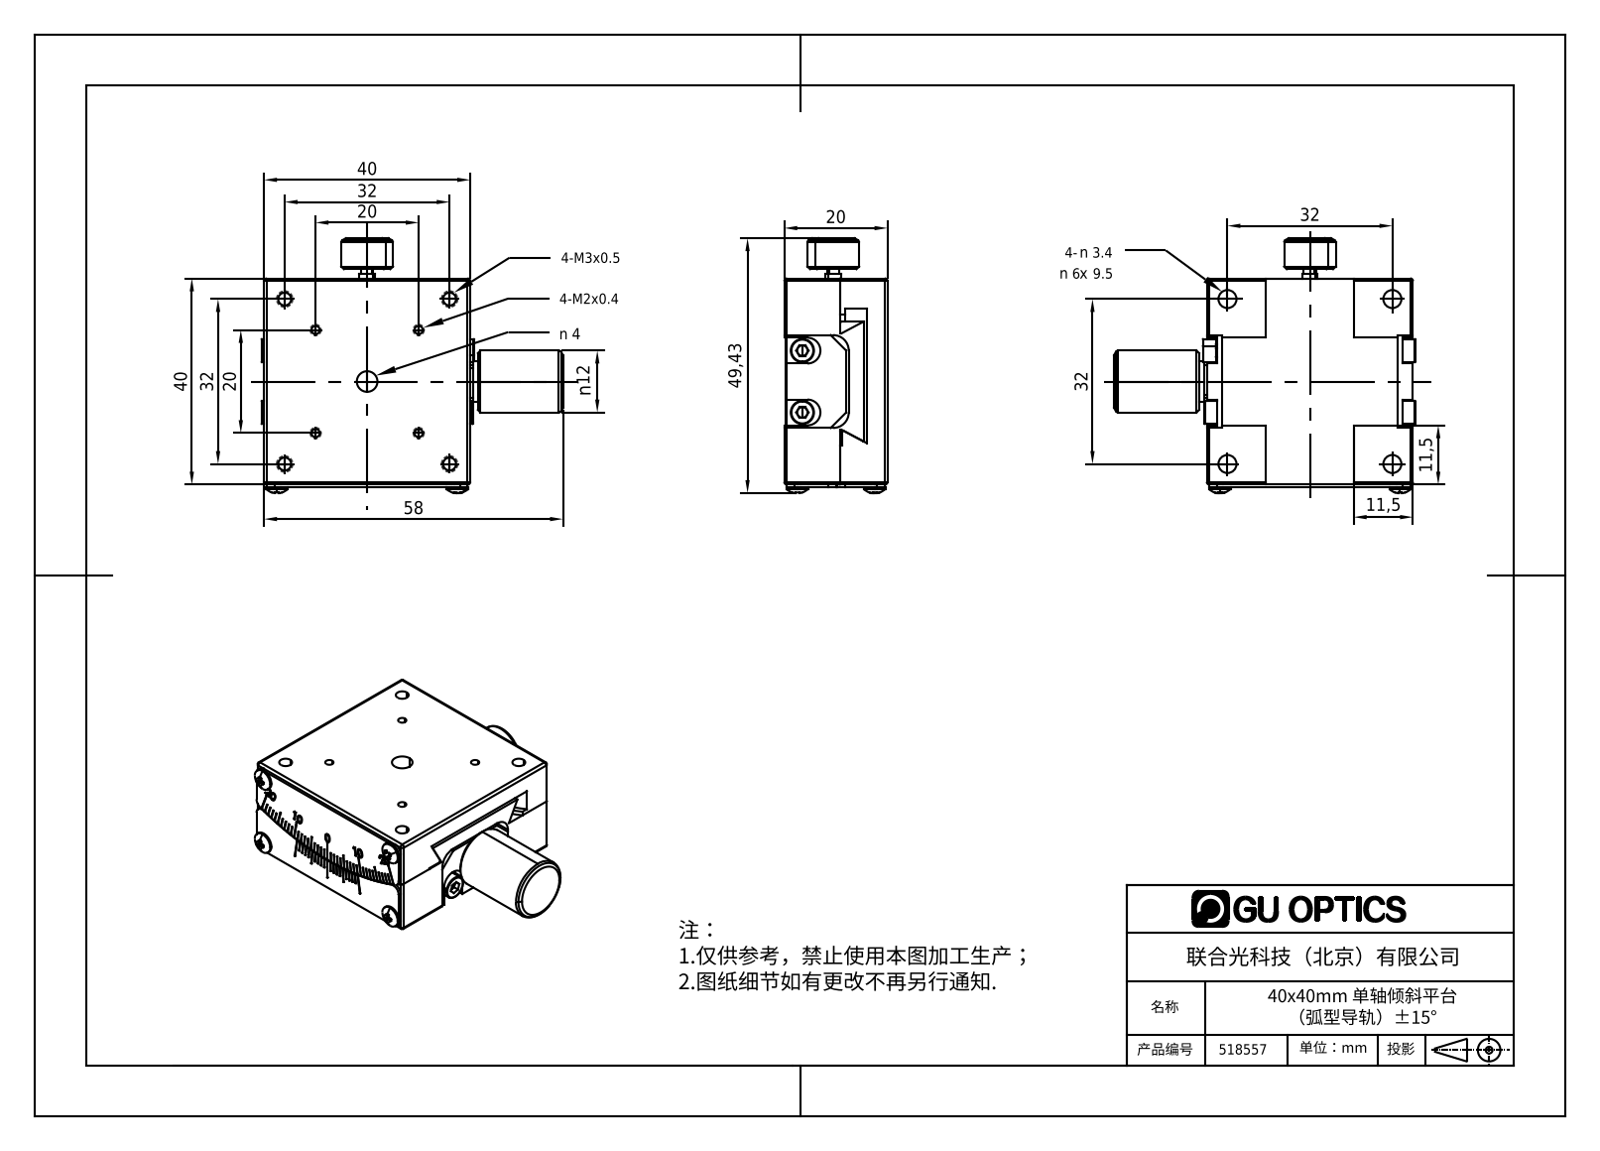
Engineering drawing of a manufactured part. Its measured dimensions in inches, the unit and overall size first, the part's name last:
Units: inches
Overall size (bounding box): 2.303 × 1.946 × 0.787
Round holes (diameter × count): ⌀0.063 ×4, ⌀0.098 ×4, ⌀0.138 ×4, ⌀0.236 ×4, ⌀0.157 ×1
Round bosses / shafts (diameter × count): ⌀0.165 ×4, ⌀0.177 ×2, ⌀0.472 ×1, ⌀0.394 ×1, ⌀0.315 ×1, ⌀0.252 ×1, ⌀0.118 ×1, ⌀0.098 ×1
Partial cylindrical surfaces — rounded edges, fillets, slot ends (radius × count): R0.02 ×12, R0.059 ×8, R0.098 ×2, R0.118 ×2, R0.177 ×1, R1.902 ×1, R1.913 ×1, R2.055 ×1
Main face-to-face distances: 0.78, 1.594, 1.575, 0.787, 0.02, 0.472, 0.295, 0.228, 1.366, 0.276
Hole centre spacings: 1.05, 0.334, 0.557, 0.787, 0.891, 1.26, 1.448, 1.113
Volume: 1.984 in³ · Surface area: 20.82 in²
Bodies: 2 solids, 835 faces (571 planar, 111 cylindrical, 153 other)
Part name (STEP PRODUCT): MXG4-40CS
STEP written by: SolidWorks 2020 (CONFIG_CONTROL_DESIGN)
